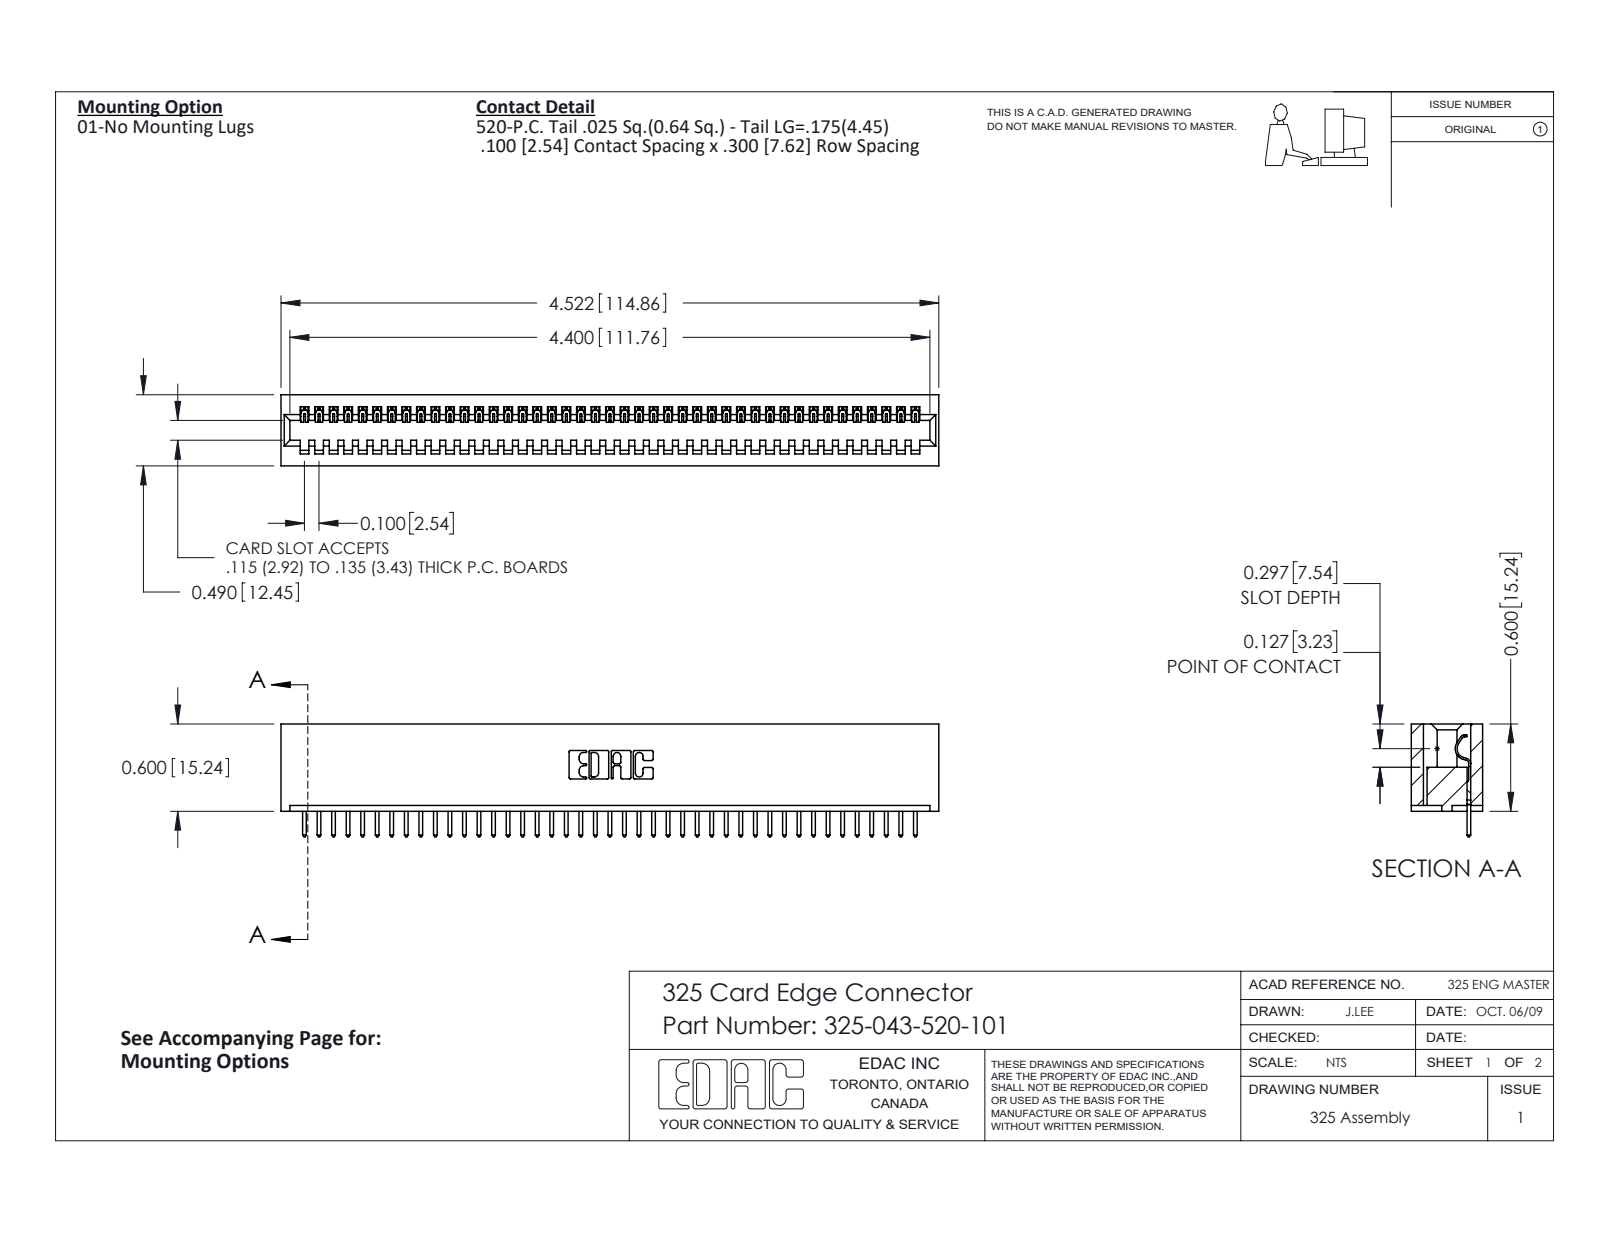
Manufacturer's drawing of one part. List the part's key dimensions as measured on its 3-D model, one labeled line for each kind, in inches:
Part name (STEP PRODUCT): 325-043-520-101; 325 Part_Lugless; 325-292-001_325-293-120
STEP written by: SolidWorks 2016 (CONFIG_CONTROL_DESIGN)
Units: inches
Bodies: 44 solids, 2600 faces (1872 planar, 728 cylindrical, 0 other)
Overall size (bounding box): 4.522 × 0.775 × 0.49
Volume: 0.918 in³ · Surface area: 25.57 in²
Partial cylindrical surfaces — rounded edges, fillets, slot ends (radius × count): R0.006 ×86, R0.01 ×86, R0.01 ×22, R0.007 ×6, R0.031 ×6, R0.026 ×3, R0.014 ×1, R0.022 ×1
Main face-to-face distances: 0.083, 0.407, 0.49, 0.3, 0.107, 0.383, 0.025, 0.325, 0.56, 0.263
